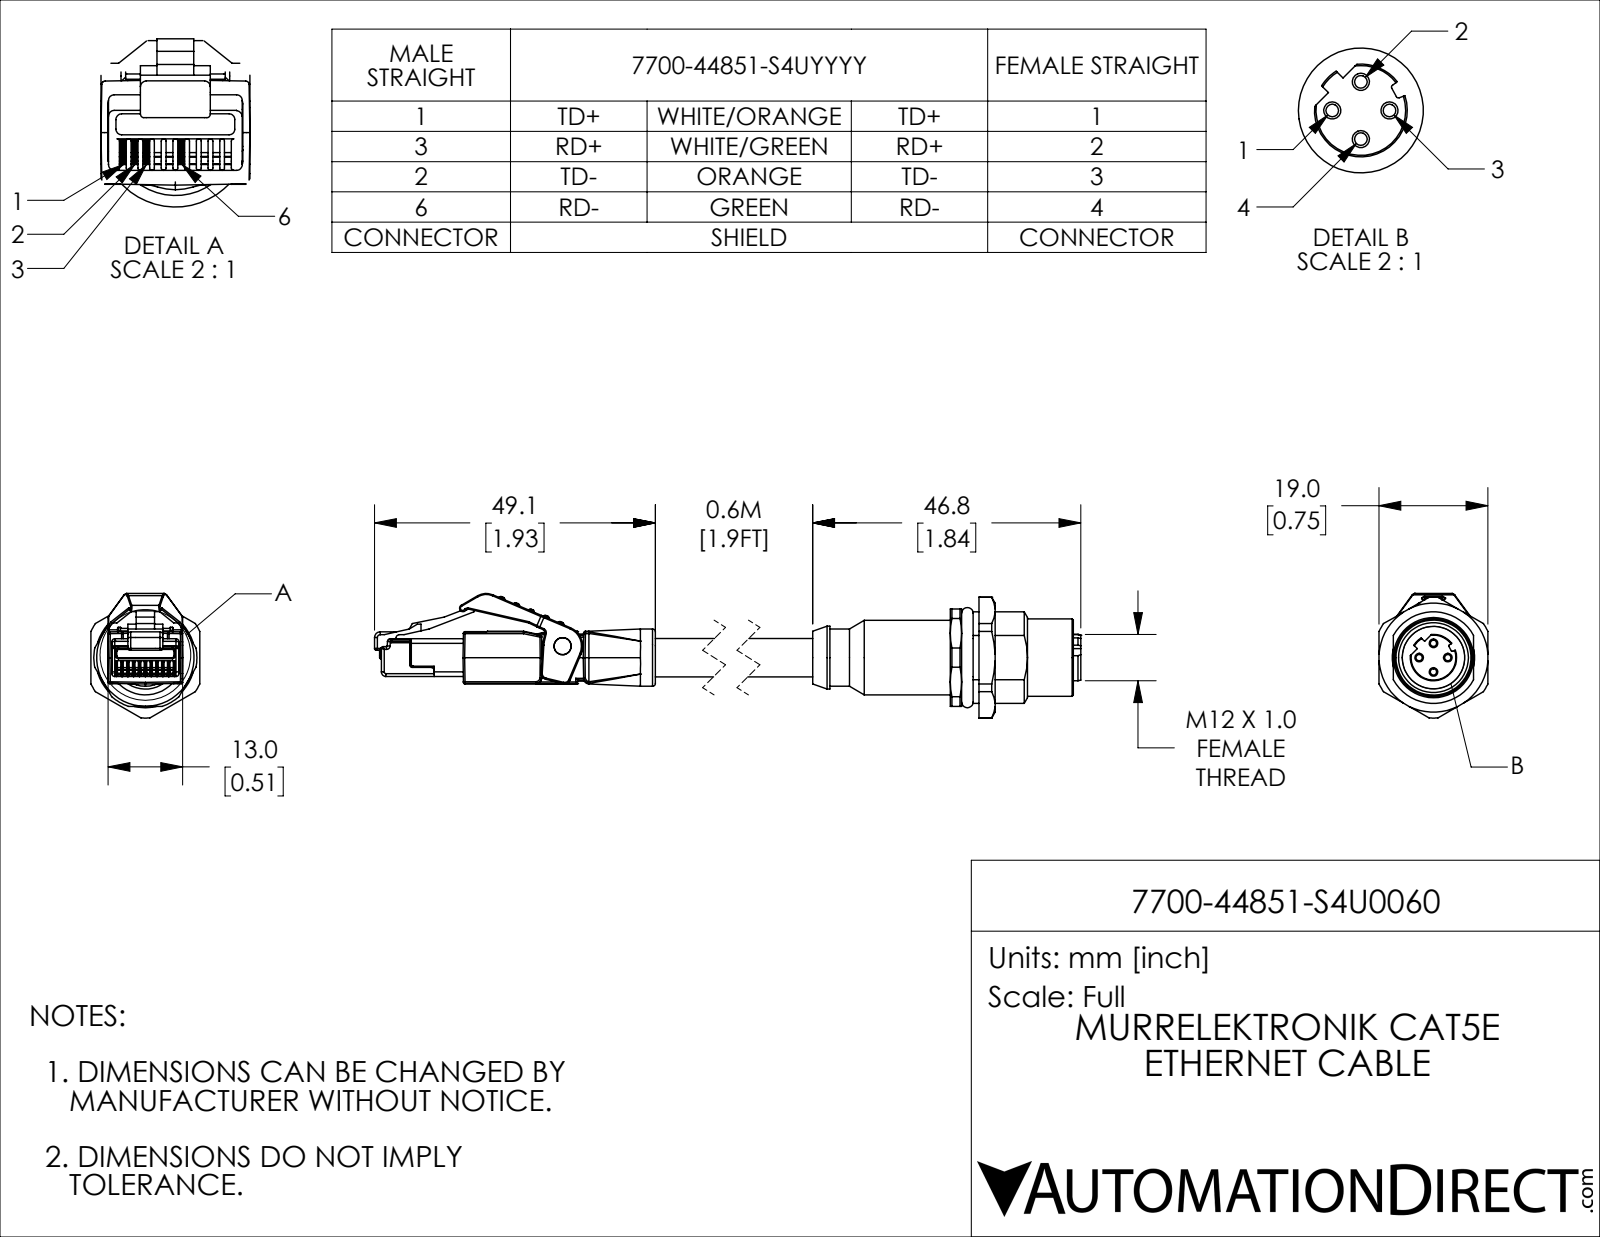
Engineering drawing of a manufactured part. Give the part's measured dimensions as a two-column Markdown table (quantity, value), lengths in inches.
| quantity | value |
| --- | --- |
| part name | 7700-44851-S4U0060; 7700-44851-S4U0060_1; 7700-44851-S4U0060_NUT; 7700-44851-S4U0060_2 |
| STEP written by | SolidWorks 2021 (CONFIG_CONTROL_DESIGN) |
| units | inches |
| bodies | 3 solids, 838 faces (325 planar, 331 cylindrical, 182 other) |
| overall size | 5.311 × 0.856 × 0.748 |
| volume | 0.793 in³ |
| surface area | 11.58 in² |
| round holes (diameter × count) | 0.043 × 4, 0.118 × 1, 0.429 × 1, 0.48 × 1, 0.566 × 1 |
| round bosses / shafts (diameter × count) | 0.531 × 1, 0.512 × 1, 0.433 × 1, 0.394 × 1, 0.264 × 1, 0.117 × 1 |
| partial cylindrical surfaces (radius × count) | 0.008 × 83, 0.012 × 64, 0.02 × 24, 0.004 × 20, 0.031 × 5, 0.039 × 5, 0.079 × 2, 0.197 × 2 |
| main face-to-face distances | 0.512, 0.362, 0.02, 0.531, 0.11, 0.198, 0.309, 0.044, 0.507, 0.024 |
| hole center spacings | 0.098, 0.139, 0.197 |
